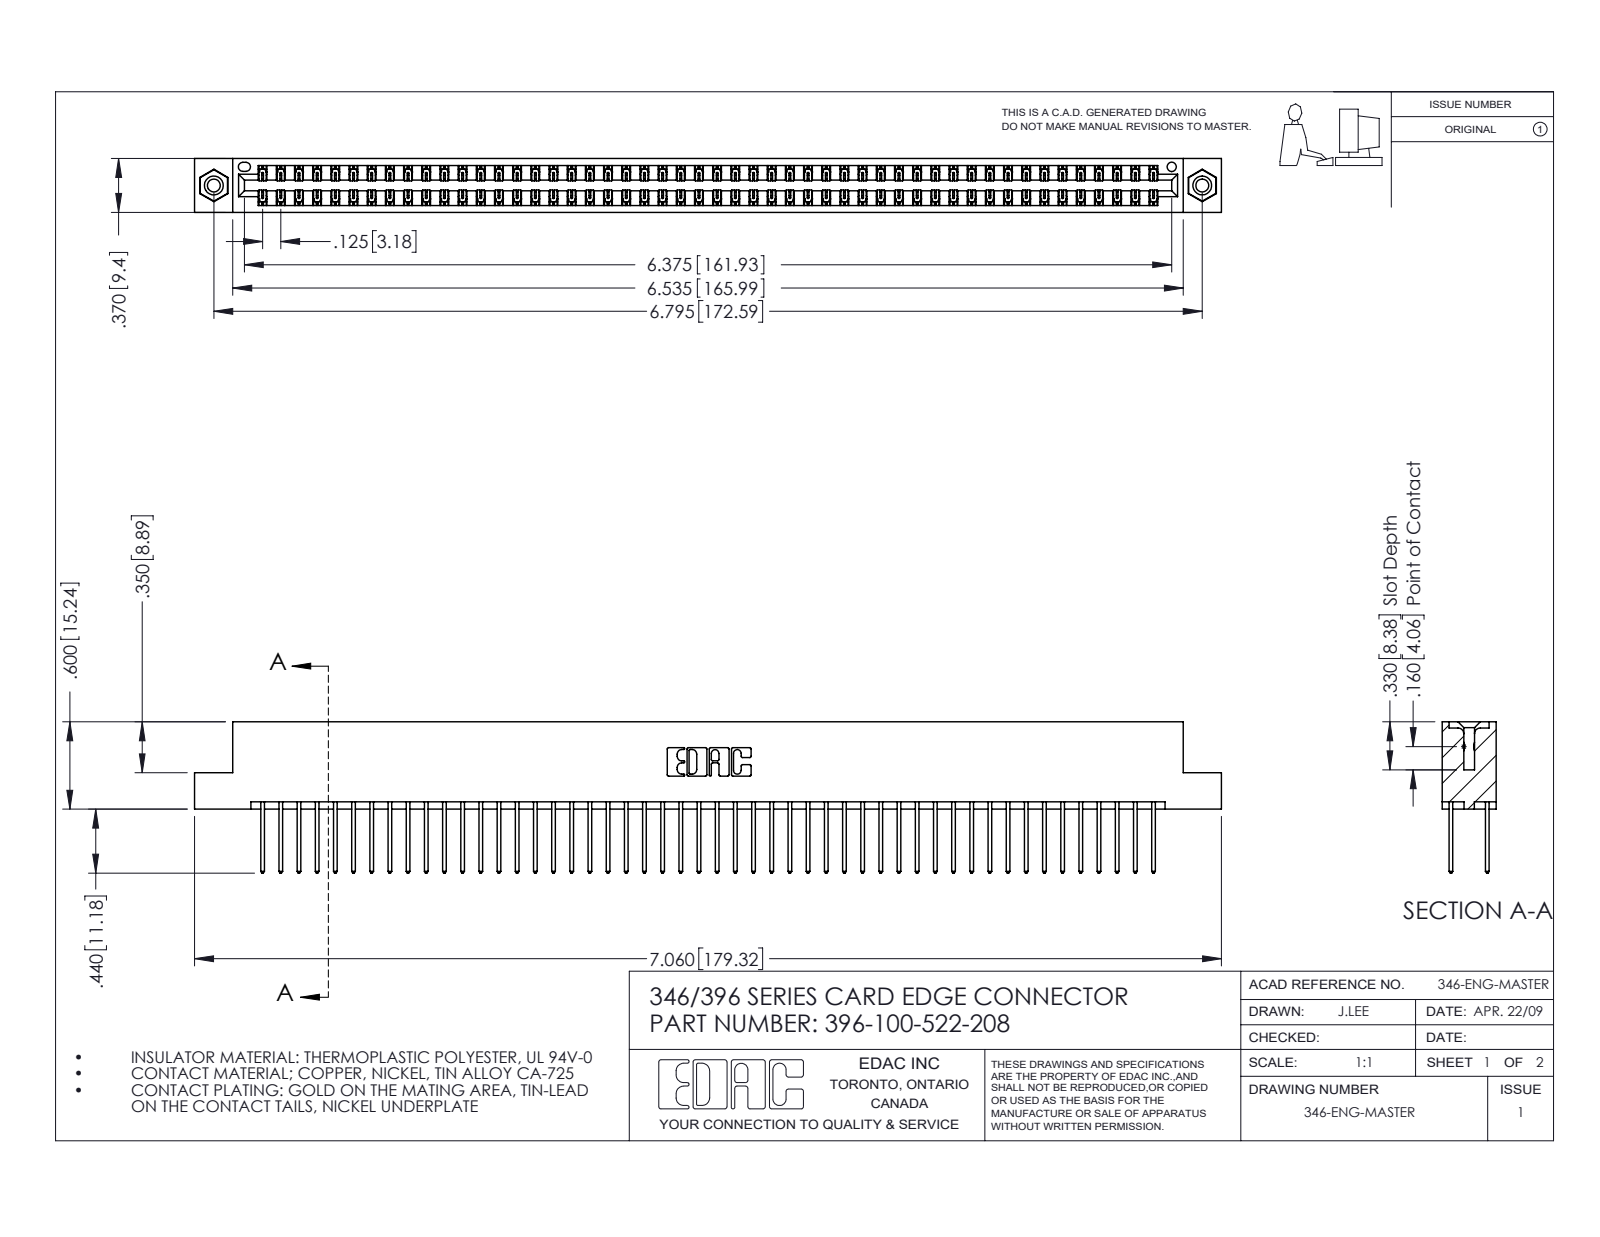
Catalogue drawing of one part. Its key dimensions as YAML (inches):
part_name: "346 Part_Flush Mounting Lugs - 0.156 Dia-TI; 345-250-001_345-250-003-102; 345-292-001_345-293-122; 396-100-522-208"
step_written_by: "SolidWorks 2016 (CONFIG_CONTROL_DESIGN)"
units: inches
bodies: {solids: 103, faces: 5382, planar: 3608, cylindrical: 1758, other: 16}
overall_size: [7.06, 1.04, 0.37]
volume: 1.086
surface_area: 39.99
round_holes:
  - {diameter: 0.089, count: 2}
  - {diameter: 0.125, count: 2}
  - {diameter: 0.156, count: 2}
  - {diameter: 0.064, count: 1}
round_bosses_or_shafts:
  - {diameter: 0.155, count: 2}
partial_cylinders:
  - {radius: 0.006, count: 150}
  - {radius: 0.01, count: 100}
  - {radius: 0.01, count: 22}
  - {radius: 0.007, count: 6}
  - {radius: 0.031, count: 6}
  - {radius: 0.026, count: 3}
  - {radius: 0.014, count: 2}
  - {radius: 0.022, count: 2}
face_to_face_distances: [0.048, 0.322, 0.25, 0.072, 0.298, 0.025, 0.37, 0.275, 0.148, 0.222]
hole_center_spacings: [0.246, 6.586, 6.795]
